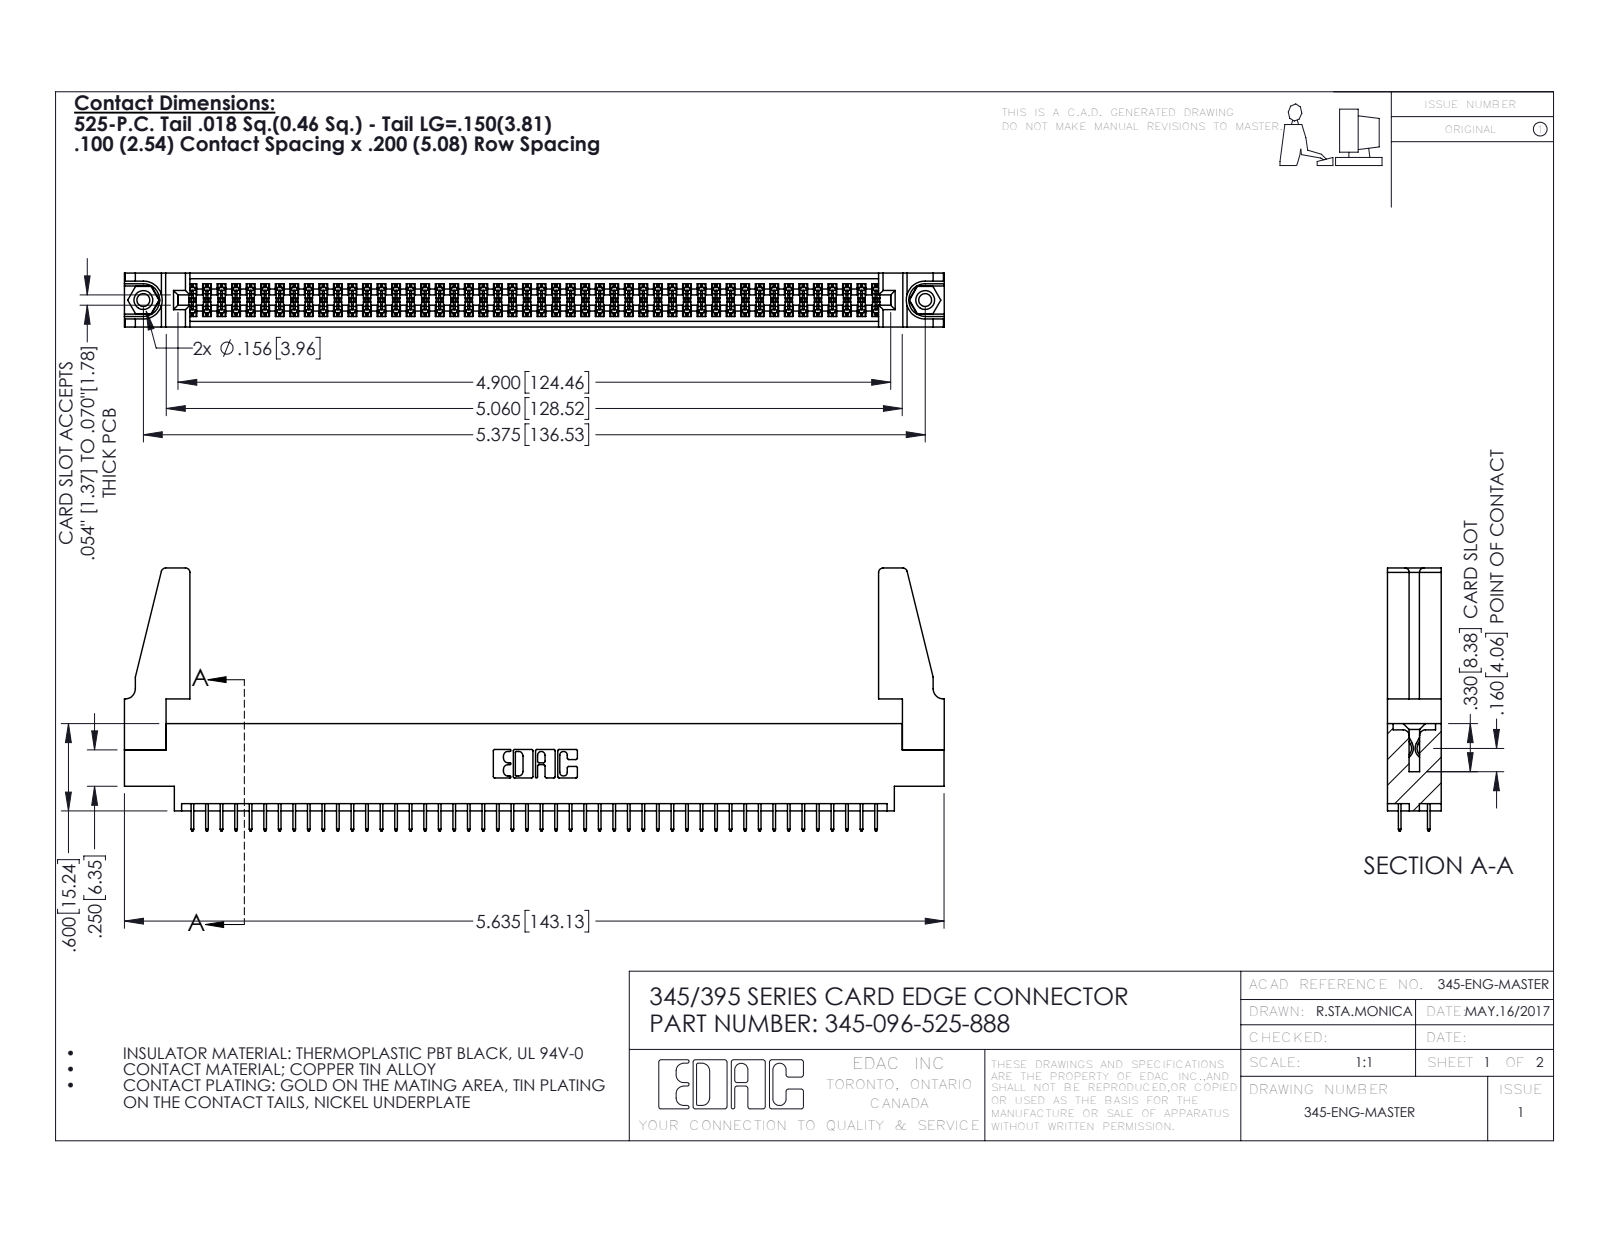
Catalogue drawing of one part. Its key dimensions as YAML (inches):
part_name: "345-096-525-888; 345-220-078_345-220-088; 345-292-001_345-293-125; 345-250-001_345-250-001-102 (+1 more)"
step_written_by: "SolidWorks 2020 (CONFIG_CONTROL_DESIGN)"
units: inches
bodies: {solids: 101, faces: 5438, planar: 3900, cylindrical: 1522, other: 16}
overall_size: [5.636, 1.807, 0.37]
volume: 1.034
surface_area: 35.87
round_holes:
  - {diameter: 0.089, count: 2}
  - {diameter: 0.125, count: 2}
  - {diameter: 0.156, count: 2}
  - {diameter: 0.064, count: 1}
round_bosses_or_shafts:
  - {diameter: 0.155, count: 2}
partial_cylinders:
  - {radius: 0.006, count: 192}
  - {radius: 0.01, count: 22}
  - {radius: 0.03, count: 8}
  - {radius: 0.007, count: 6}
  - {radius: 0.031, count: 6}
  - {radius: 0.026, count: 3}
  - {radius: 0.014, count: 2}
  - {radius: 0.019, count: 2}
face_to_face_distances: [0.072, 0.298, 0.37, 0.2, 0.098, 0.272, 0.025, 0.225, 0.175, 0.072]
hole_center_spacings: [0.27, 5.139, 5.375]
